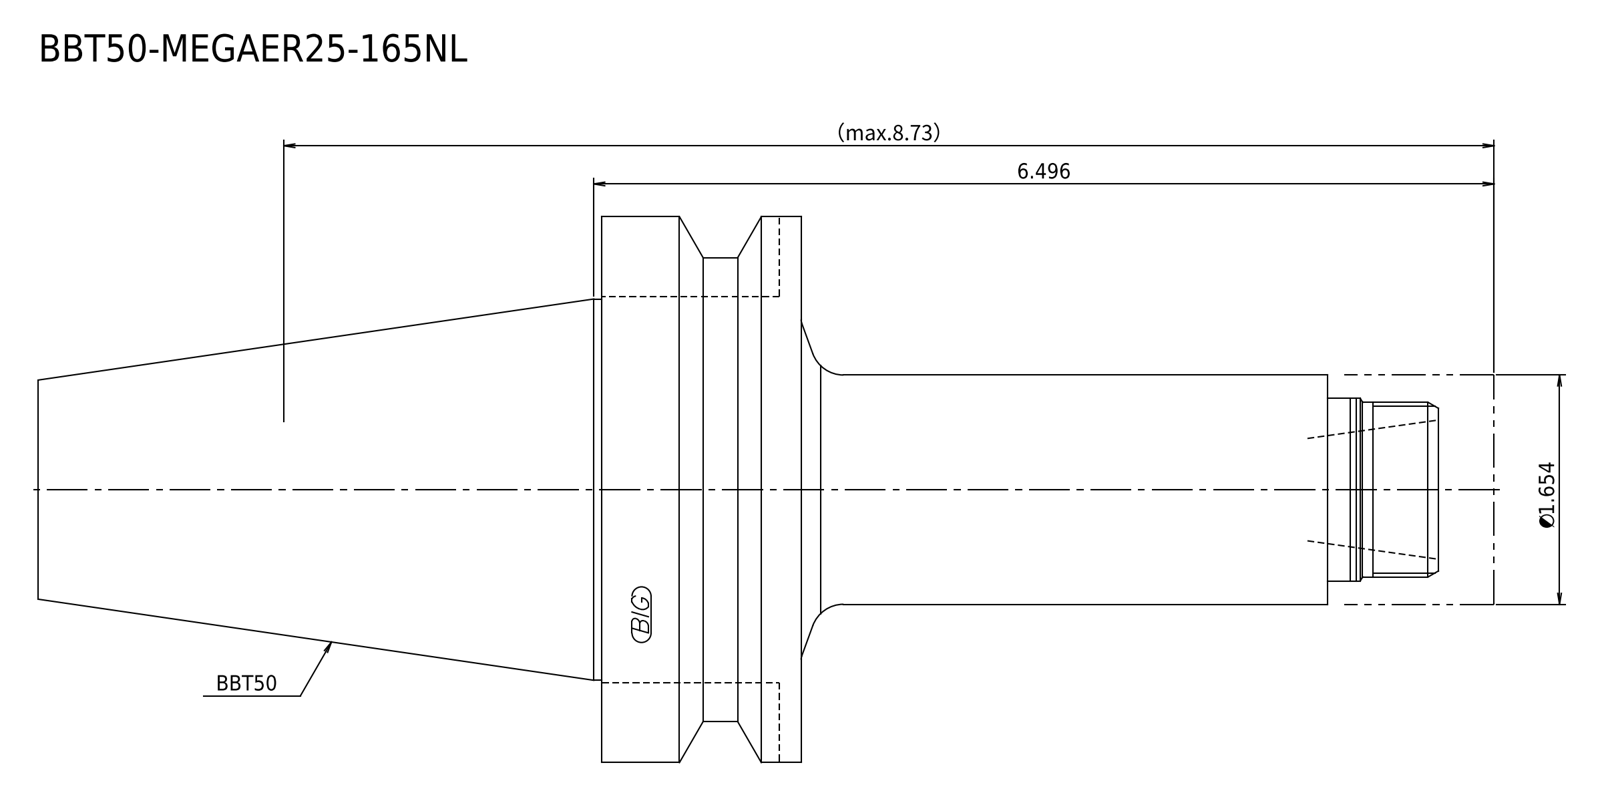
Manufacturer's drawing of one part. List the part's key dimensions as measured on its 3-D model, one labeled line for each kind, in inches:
STEP written by: Kubotek KeyCreator 2011 V10.0.2 (22737) (automotive_design)
Units: inches
Bodies: 2 solids, 21 faces (7 planar, 8 cylindrical, 6 other)
Overall size (bounding box): 266.8 × 100 × 100
Volume: 711 207 in³ · Surface area: 65 221 in²
Round bosses / shafts (diameter × count): ⌀100 ×1, ⌀85 ×1, ⌀69.85 ×1, ⌀42 ×1, ⌀33.5 ×1, ⌀32 ×1
Main face-to-face distances: 36.5, 99.5, 136, 27.5, 127, 163.5, 266.8, 239.3, 139.8, 103.3
